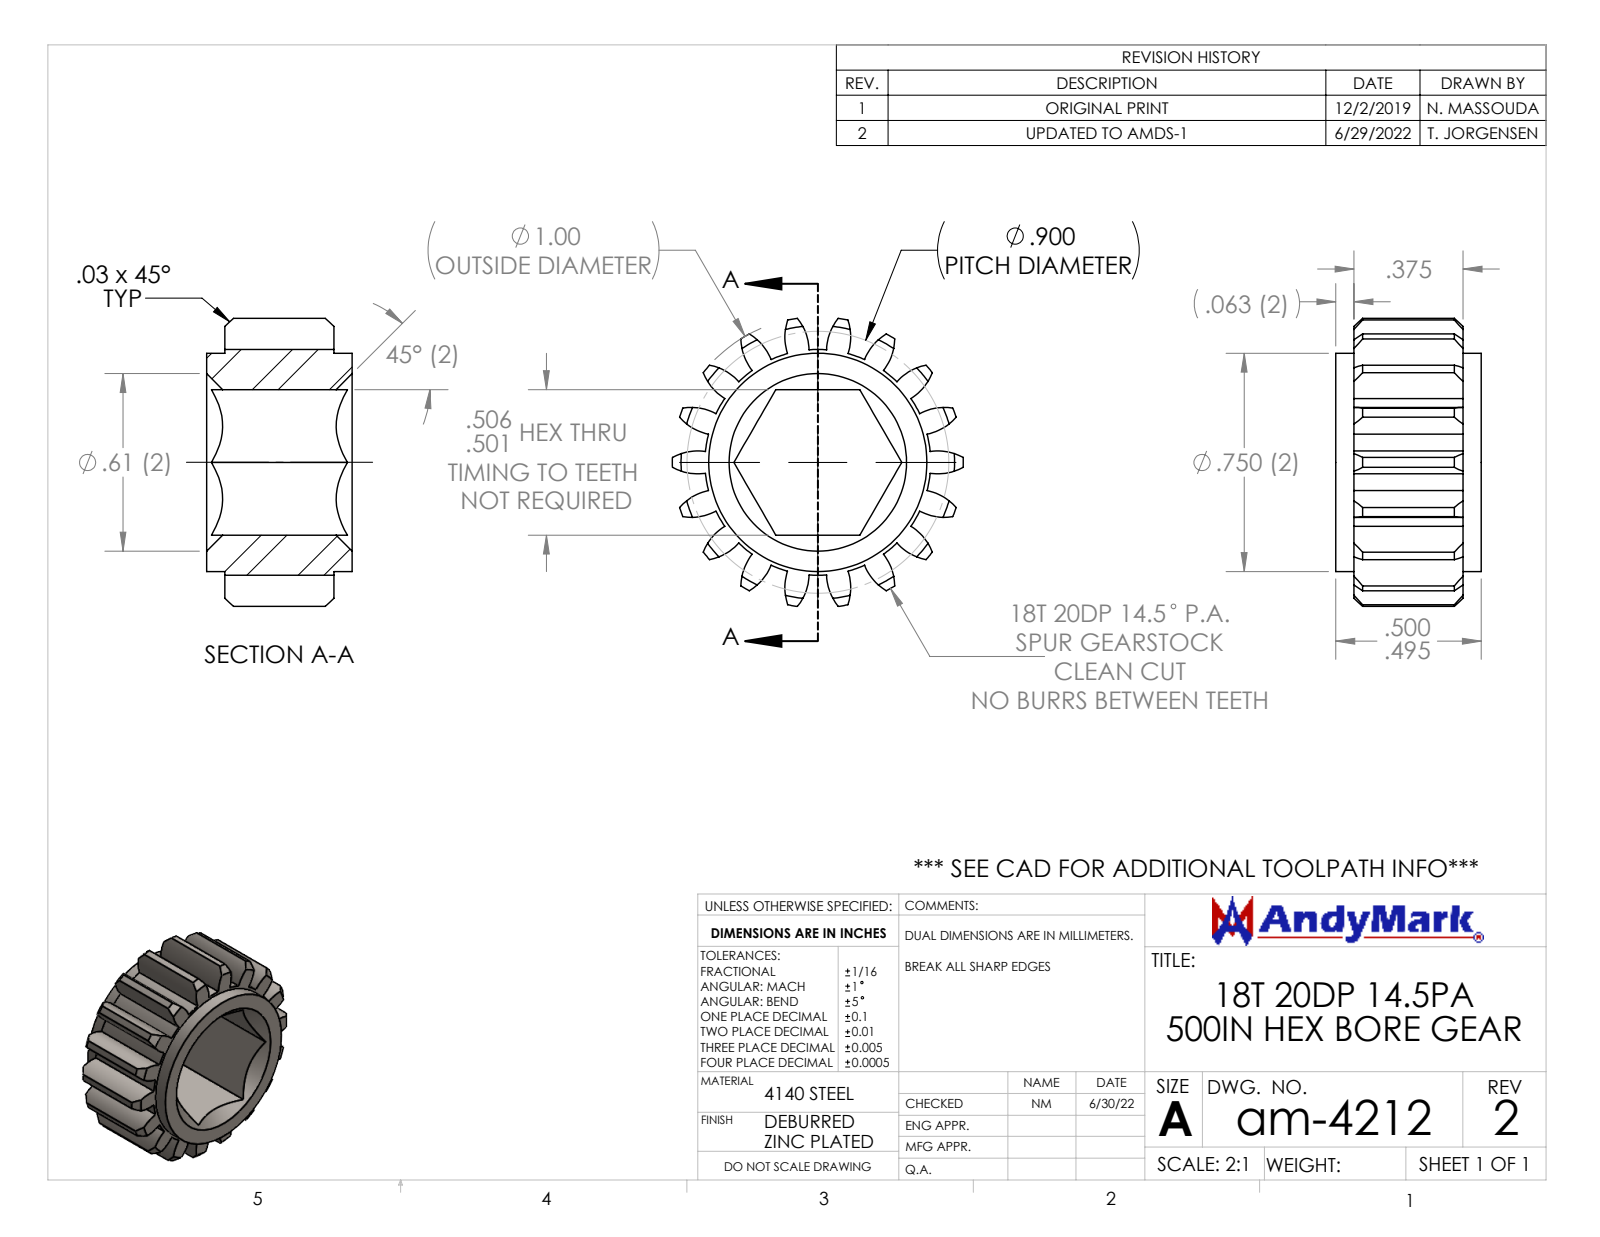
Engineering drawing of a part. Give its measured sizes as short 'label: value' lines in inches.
name: am-4212 18T 20DP 500hex 375 FW
written by: SolidWorks 2022 (CONFIG_CONTROL_DESIGN)
unit: in
bodies: 1 solid, 147 faces (10 planar, 79 cylindrical, 58 other)
size: 1 × 0.99 × 0.5
volume: 0.171 in³; area: 4.032 in²
bosses: 1× ⌀0.75
rounds: 36× R0.18, 1× R0.388, 1× R0.5
face distances: 0.5, 0.438, 0.062, 0.063, 0.375, 0.437
